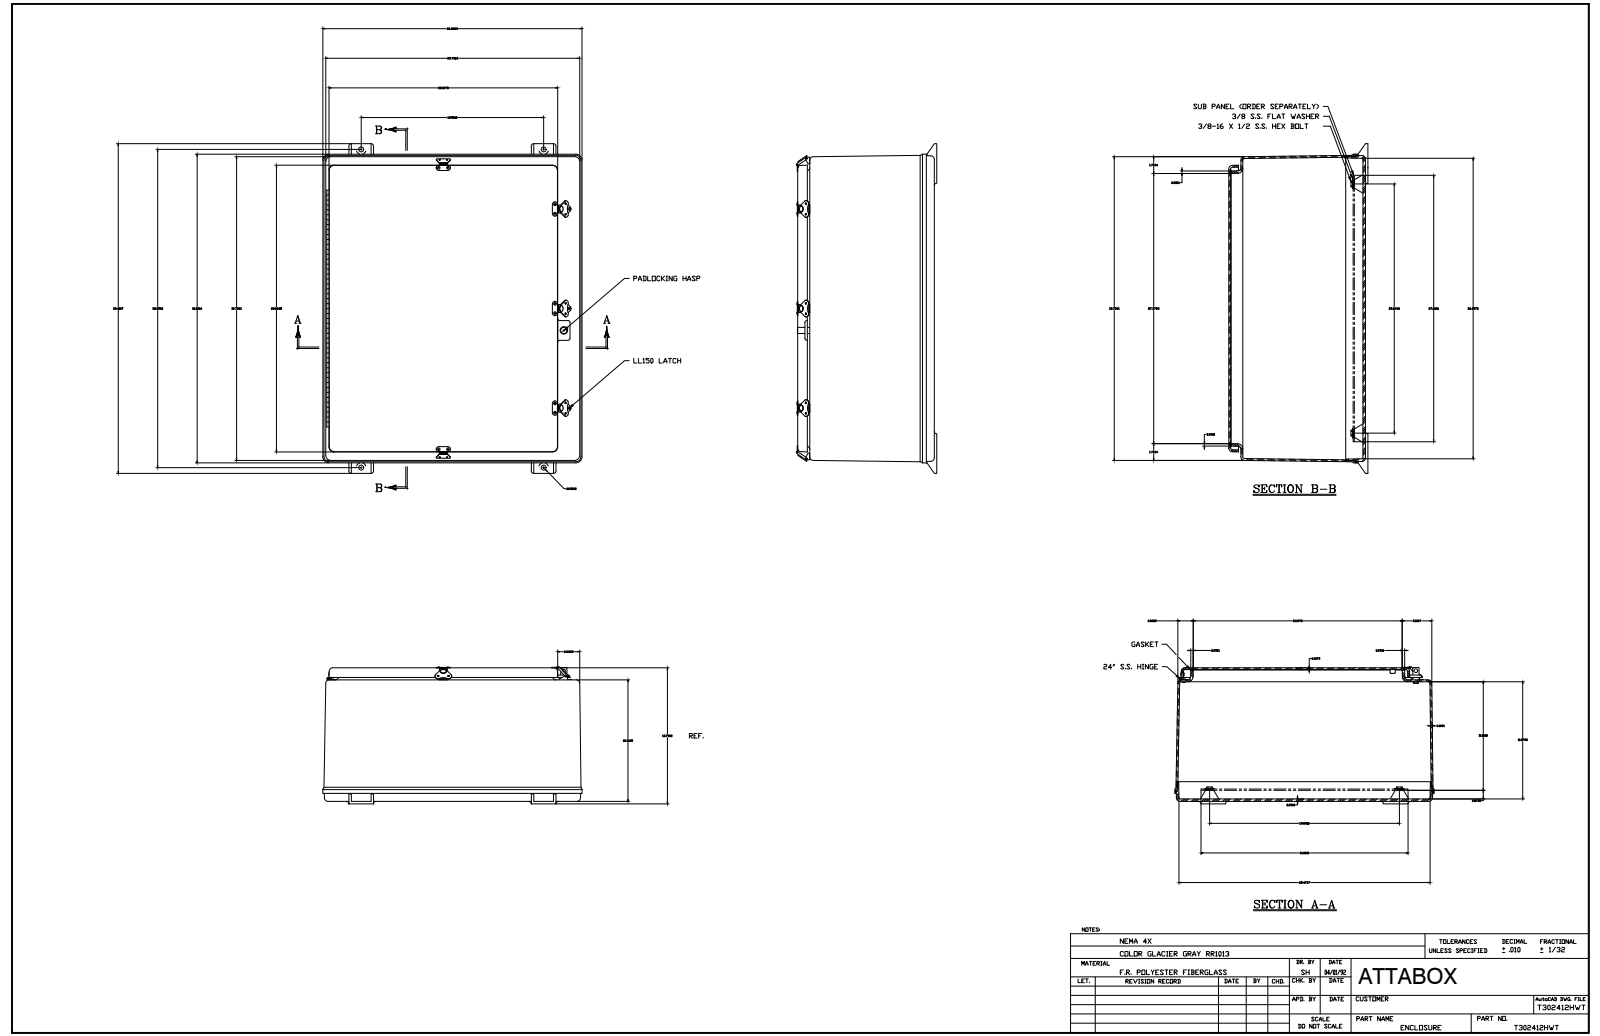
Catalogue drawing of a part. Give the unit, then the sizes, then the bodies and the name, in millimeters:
Units: millimetres
Overall size (bounding box): 848.5 × 667.5 × 358.5
Round holes (diameter × count): ⌀3.3 ×36, ⌀1.6 ×20, ⌀3.5 ×10, ⌀4.7 ×10, ⌀1.7 ×4, ⌀1.7 ×4, ⌀14.3 ×4, ⌀4 ×3, ⌀3.4 ×2, ⌀7.1 ×2, ⌀13 ×2, ⌀13 ×2
Round bosses / shafts (diameter × count): ⌀3.6 ×20, ⌀7.5 ×8, ⌀12.7 ×5, ⌀5.1 ×3, ⌀3.4 ×2, ⌀6.4 ×1, ⌀5.1 ×1, ⌀3.4 ×1
Partial cylindrical surfaces — rounded edges, fillets, slot ends (radius × count): R0.3 ×127, R6.4 ×24, R7.9 ×23, R0.8 ×20, R9.5 ×13, R4.7 ×12, R12.7 ×12, R3.2 ×10
Main face-to-face distances: 4.7, 6.4, 4.8, 343.7, 337.3, 338.9, 332.6, 312.7, 31, 308
Hole centre spacings: 190.5, 393.7, 256.4, 25.4, 203.2, 584.2, 88.6, 95.4
Volume: 11 150 000 mm³ · Surface area: 4 490 000 mm²
Bodies: 63 solids, 1763 faces (659 planar, 712 cylindrical, 392 other)
Part name (STEP PRODUCT): T302412HWT
STEP written by: SolidWorks 2018 (AUTOMOTIVE_DESIGN)
